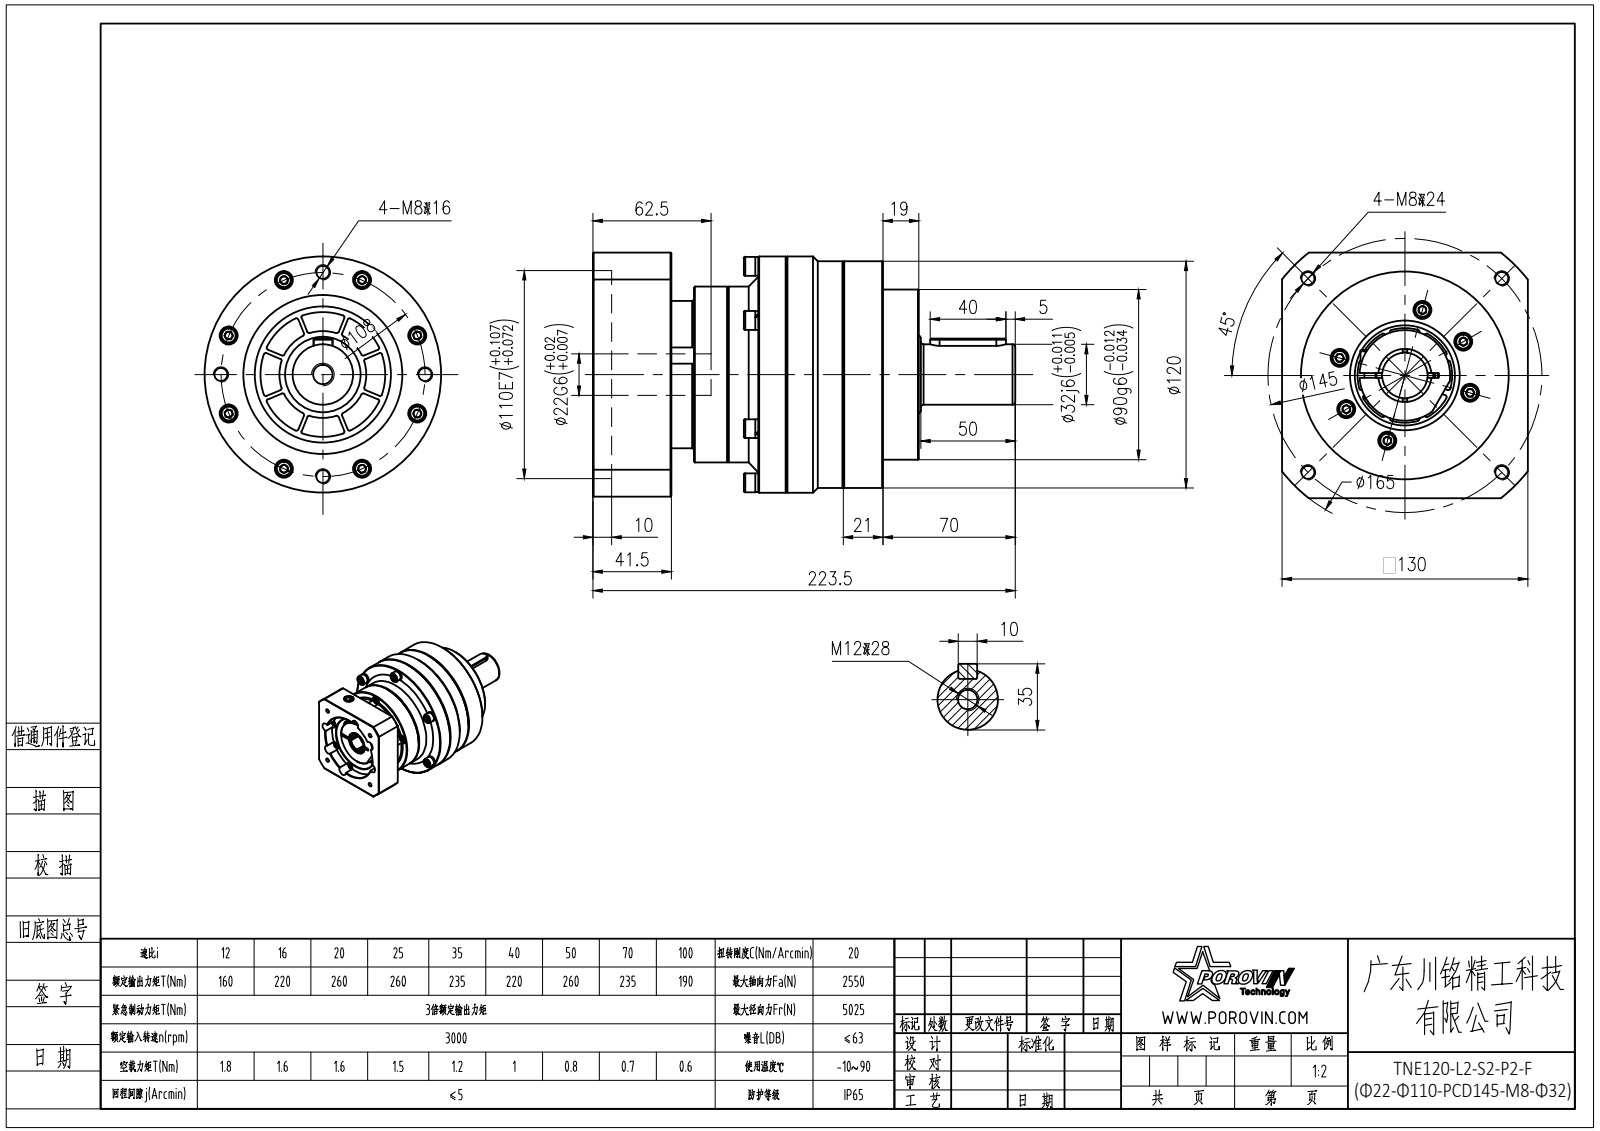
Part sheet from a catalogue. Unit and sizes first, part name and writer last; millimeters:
Units: millimetres
Overall size (bounding box): 223.5 × 130 × 130
Round holes (diameter × count): ⌀4.2 ×22, ⌀5.4 ×10, ⌀5.5 ×10, ⌀9.5 ×10, ⌀6.8 ×8, ⌀5 ×7, ⌀6.6 ×6, ⌀6.68 ×6, ⌀9 ×2, ⌀10.2 ×2, ⌀6.5 ×1, ⌀13 ×1
Round bosses / shafts (diameter × count): ⌀8.5 ×22, ⌀5 ×22, ⌀8 ×10, ⌀10 ×7, ⌀6 ×7, ⌀9.88 ×6, ⌀20 ×2, ⌀125 ×1
Partial cylindrical surfaces — rounded edges, fillets, slot ends (radius × count): R1 ×32, R5 ×2, R5.5 ×1, R82.5 ×1
Main face-to-face distances: 30, 61, 91, 31, 3, 130, 19, 33, 94, 64
Hole centre spacings: 56, 57.25, 40.75, 76.33, 99.16, 9.7, 42.86, 43.34
Volume: 1 515 000 mm³ · Surface area: 264 142 mm²
Bodies: 57 solids, 1490 faces (639 planar, 496 cylindrical, 355 other)
Part name (STEP PRODUCT): hexagon socket head cap screws gb_GB_FASTENER_SCREWS_HSHCS M6X20-N; hexagon socket head cap screws gb_GB_FASTENER_SCREWS_HSHCS M5X25-N; 二级齿圈 KS115 外形图; hex socket set screws with flat point gb_GB_FASTENER_SCREWS_HSFP M12X16-N (+6 more)
STEP written by: SolidWorks 2016 (CONFIG_CONTROL_DESIGN)
